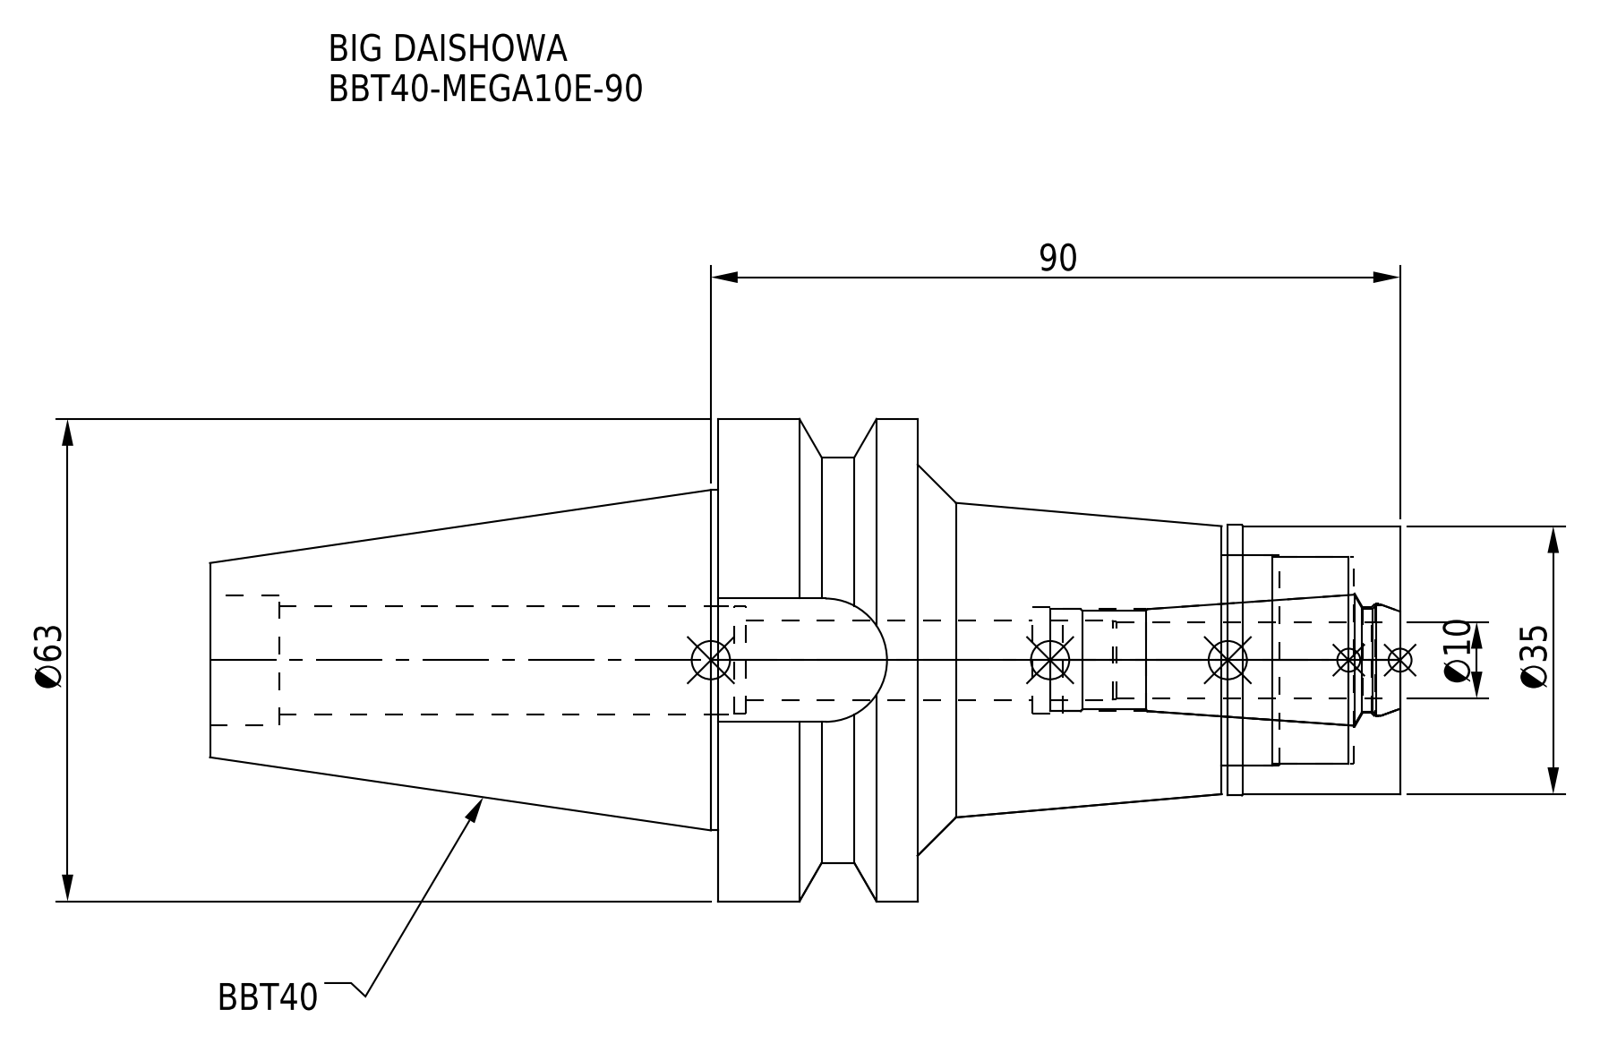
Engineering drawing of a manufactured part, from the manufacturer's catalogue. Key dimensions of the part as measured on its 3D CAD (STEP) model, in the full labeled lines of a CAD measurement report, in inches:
Part name (STEP PRODUCT): BBT40ME10090-100_ASM.stp; DXF_TEMP_ASSY_ASM_4_ASM.stp; BBT40-MEGA10E-90-100.stp; BBT40-MEGA10E-90 (+3 more)
STEP written by: SolidWorks 2019 (CONFIG_CONTROL_DESIGN)
Units: inches
Bodies: 2 solids, 81 faces (21 planar, 40 cylindrical, 20 other)
Overall size (bounding box): 6.118 × 2.48 × 2.48
Volume: 11.13 in³ · Surface area: 56.13 in²
Round holes (diameter × count): ⌀0.409 ×1, ⌀0.524 ×1, ⌀0.543 ×1, ⌀0.547 ×1, ⌀0.551 ×1, ⌀0.559 ×1, ⌀0.579 ×1, ⌀0.669 ×1, ⌀1.063 ×1, ⌀1.083 ×1
Round bosses / shafts (diameter × count): ⌀2.48 ×1, ⌀2.087 ×1, ⌀1.75 ×1, ⌀1.39 ×1, ⌀1.378 ×1
Partial cylindrical surfaces — rounded edges, fillets, slot ends (radius × count): R0.317 ×1
Main face-to-face distances: 1.024, 2.48, 3.504, 0.886, 1.594, 2.618, 0.917, 0.031, 1.563, 2.587
